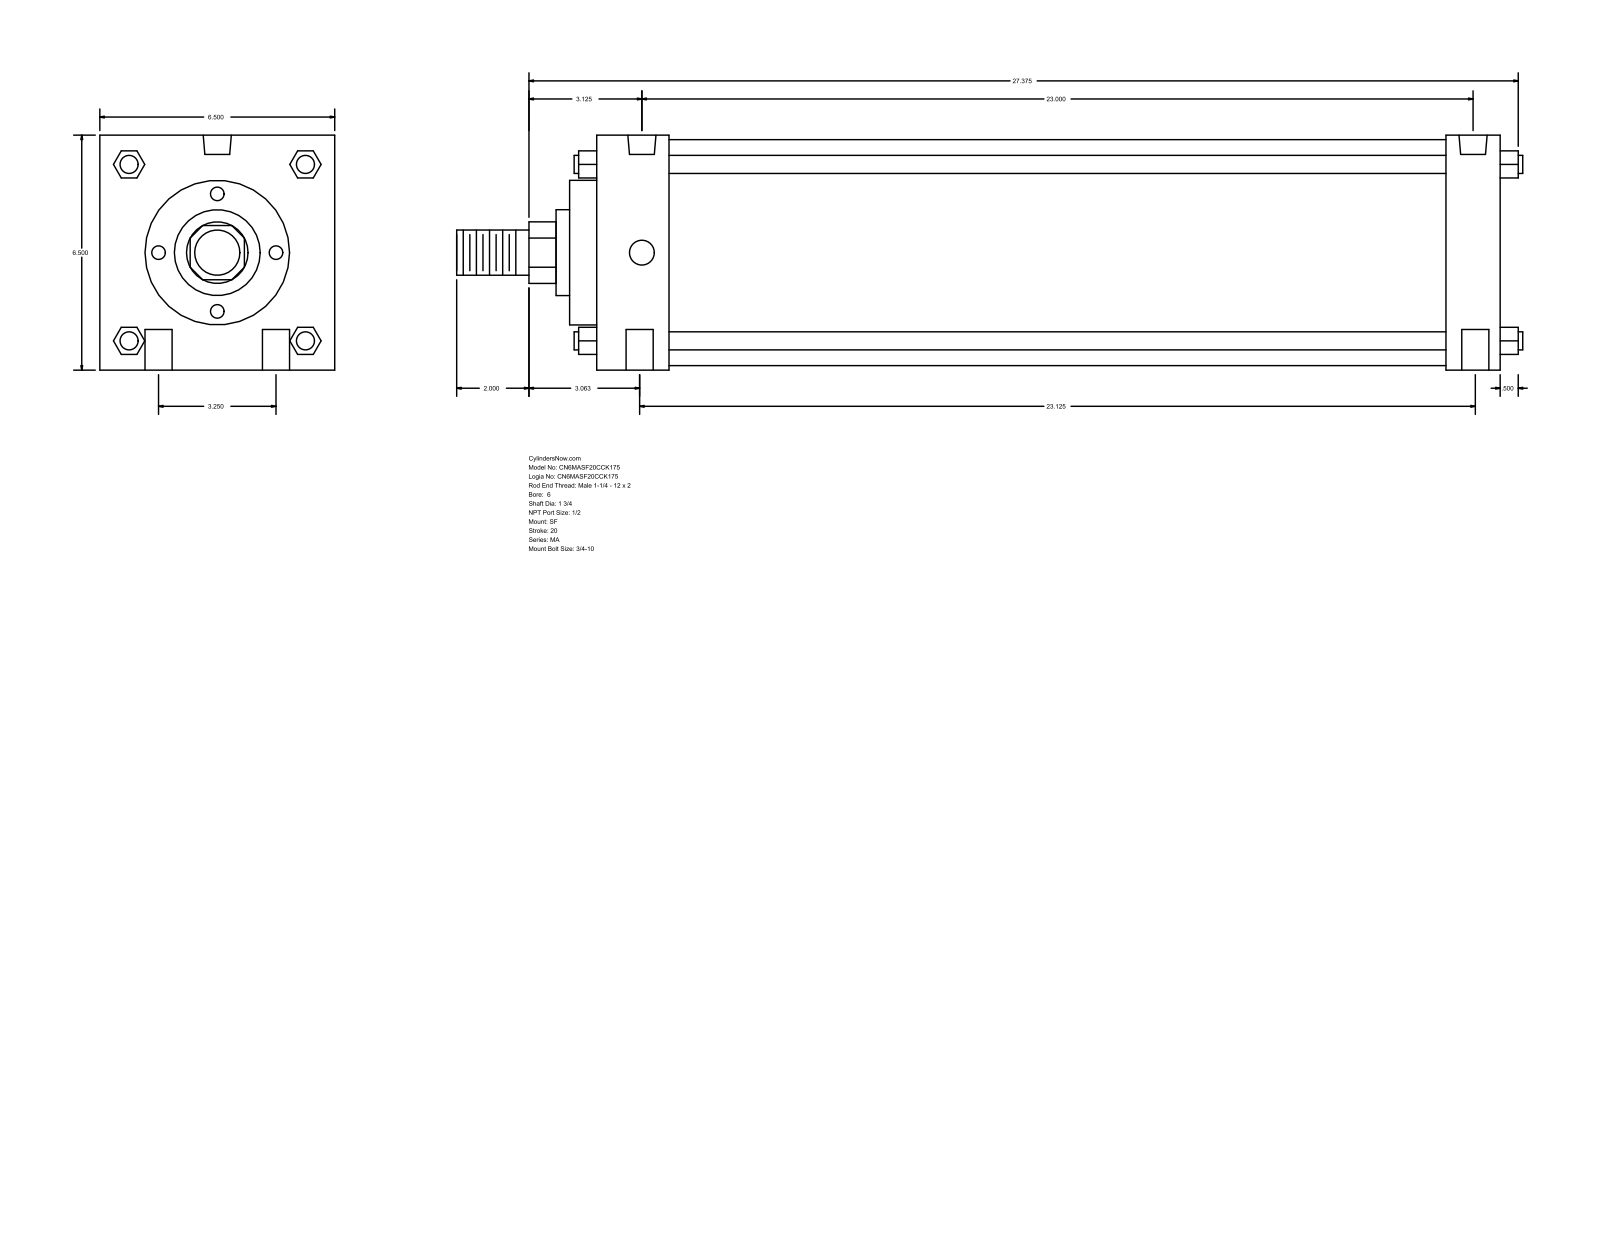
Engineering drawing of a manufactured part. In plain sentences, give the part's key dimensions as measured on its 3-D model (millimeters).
The part is named "MA_SF__0600_1.75". Its 3-D file was written by "GSSL Pune (CONFIG_CONTROL_DESIGN)". It is 0 solids with 126 faces: 95 planar, 31 cylindrical and 0 other. Overall it measures 749.3 by 165.1 by 165.1 millimeters. Round holes: 4 of diameter 19.05, 2 of diameter 17.46, 2 of diameter 19.77. Round bosses or shafts: 4 of diameter 12.7, 1 of diameter 158.75, 1 of diameter 101.6, 1 of diameter 60.33, 1 of diameter 44.45, 1 of diameter 31.75. Partial cylindrical surfaces (rounded edges, fillets, slot ends): 1 of radius 21.63. The main face-to-face distances are 165.1, 635, 19.05, 50.8, 38.1, 596.9, 546.1, 584.2, 69.85, 615.95. The hole center spacings are 41.3, 82.54, 584.2, 587.23, 587.24, 587.37, 593.14.
